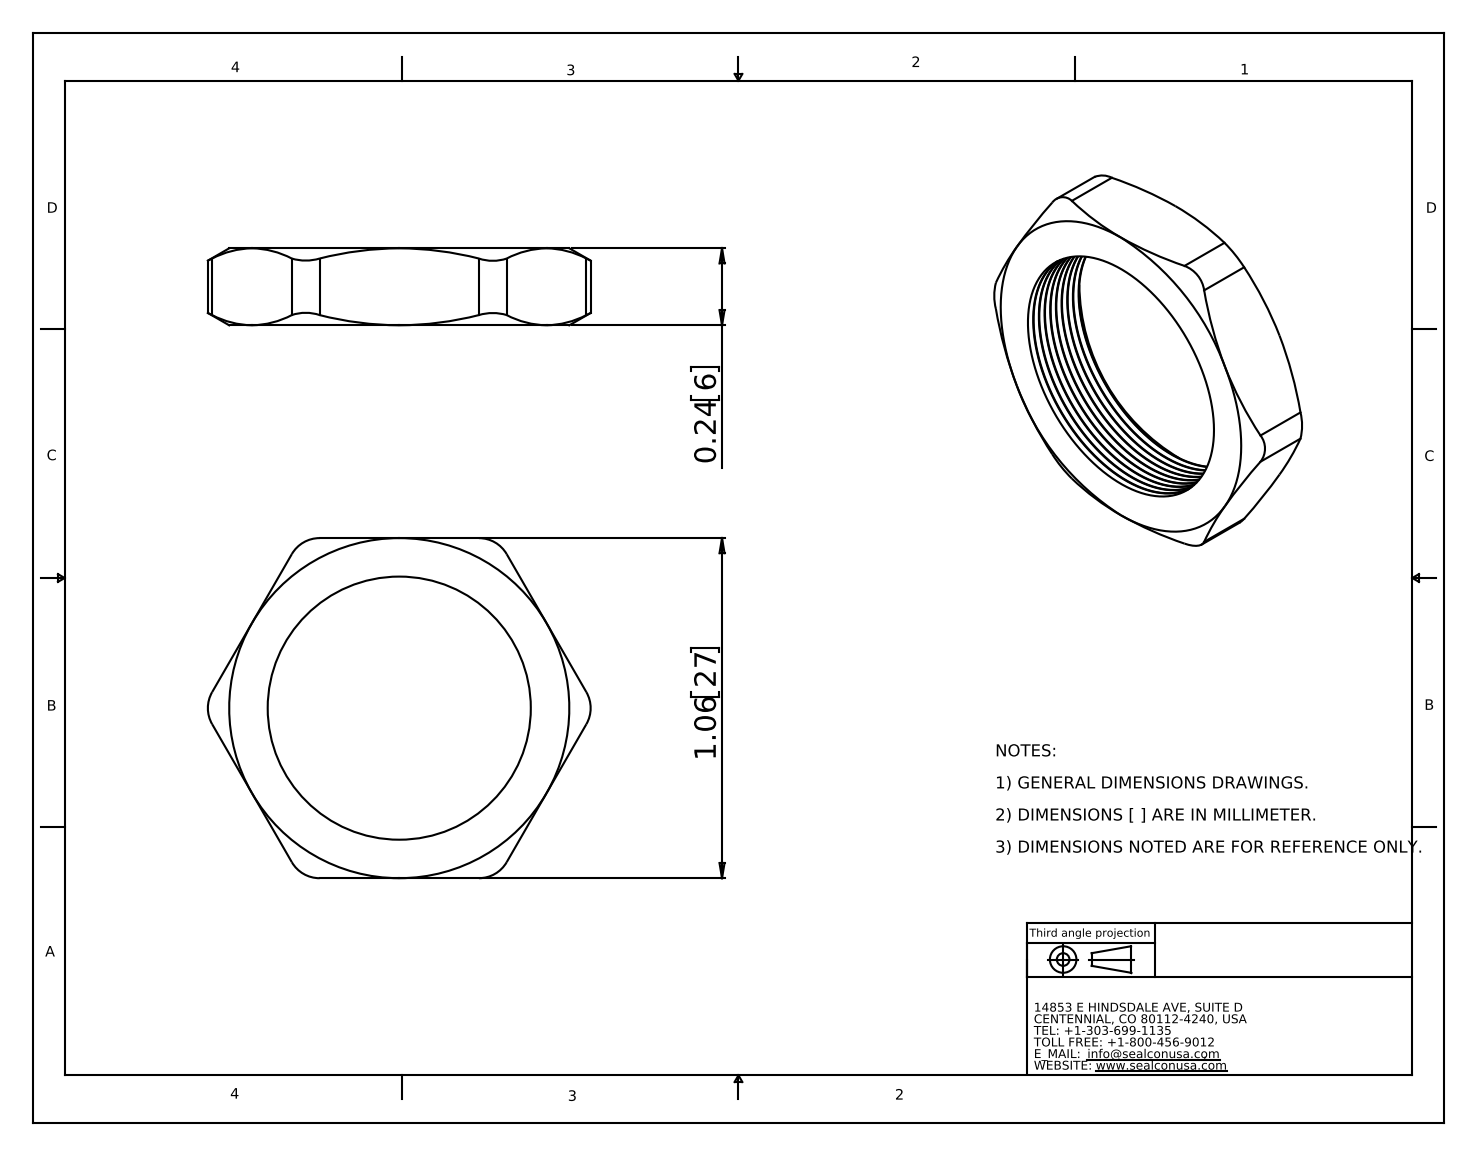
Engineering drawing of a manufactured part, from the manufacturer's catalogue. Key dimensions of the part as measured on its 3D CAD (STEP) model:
Part name (STEP PRODUCT): NN-13-GY
STEP written by: SolidWorks 2007 (CONFIG_CONTROL_DESIGN)
Units: inches
Bodies: 1 solid, 87 faces (8 planar, 25 cylindrical, 54 other)
Overall size (bounding box): 1.193 × 1.06 × 0.24
Volume: 0.098 in³ · Surface area: 2.85 in²
Round holes (diameter × count): ⌀0.82 ×1
Partial cylindrical surfaces — rounded edges, fillets, slot ends (radius × count): R0.1 ×6
Main face-to-face distances: 1.06, 0.24
